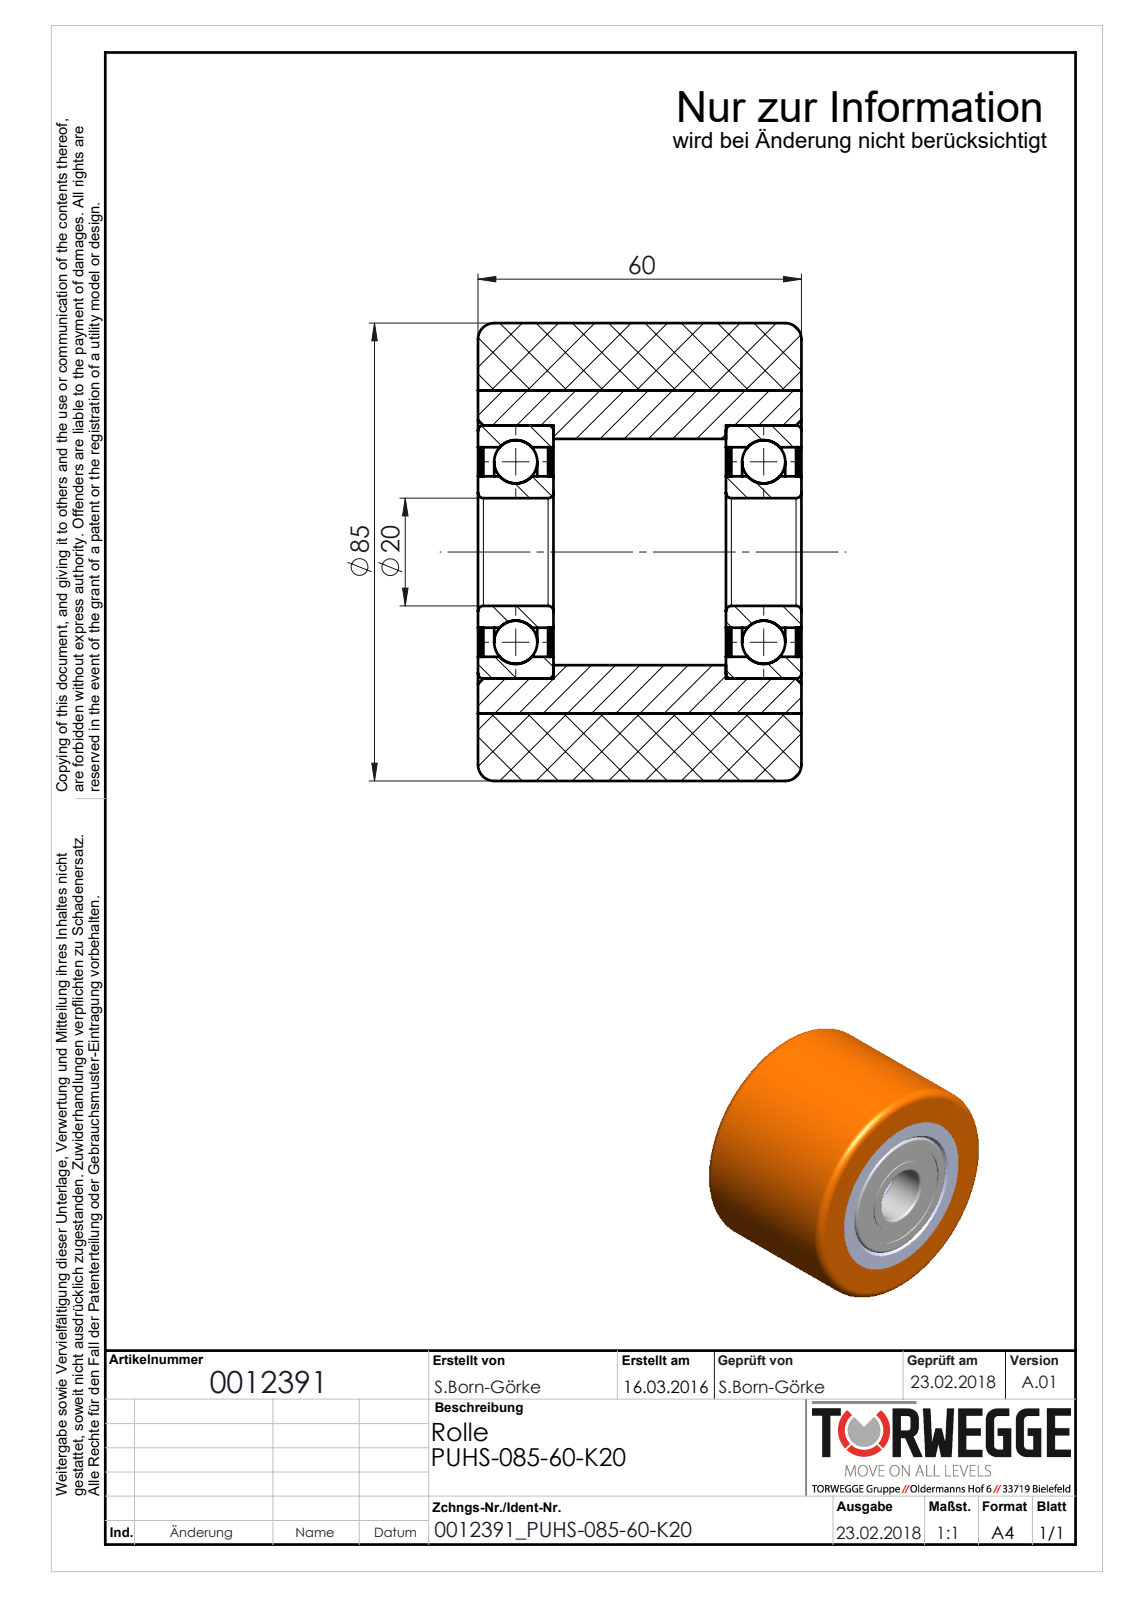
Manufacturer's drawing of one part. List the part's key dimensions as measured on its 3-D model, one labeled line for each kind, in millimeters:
Part name (STEP PRODUCT): 0012391_PUHS-085-60-K20
STEP written by: SolidWorks 2016 (AUTOMOTIVE_DESIGN)
Units: millimetres
Bodies: 12 solids, 118 faces (22 planar, 52 cylindrical, 44 other)
Overall size (bounding box): 85 × 85 × 60
Volume: 279 276 mm³ · Surface area: 80 147 mm²
Round holes (diameter × count): ⌀20 ×1, ⌀28.1 ×1, ⌀38.9 ×1, ⌀42 ×1, ⌀47 ×1, ⌀60 ×1
Round bosses / shafts (diameter × count): ⌀85 ×1
Main face-to-face distances: 0.5, 46, 60, 13, 1, 13.5, 46.5, 12.5, 45.5, 14
